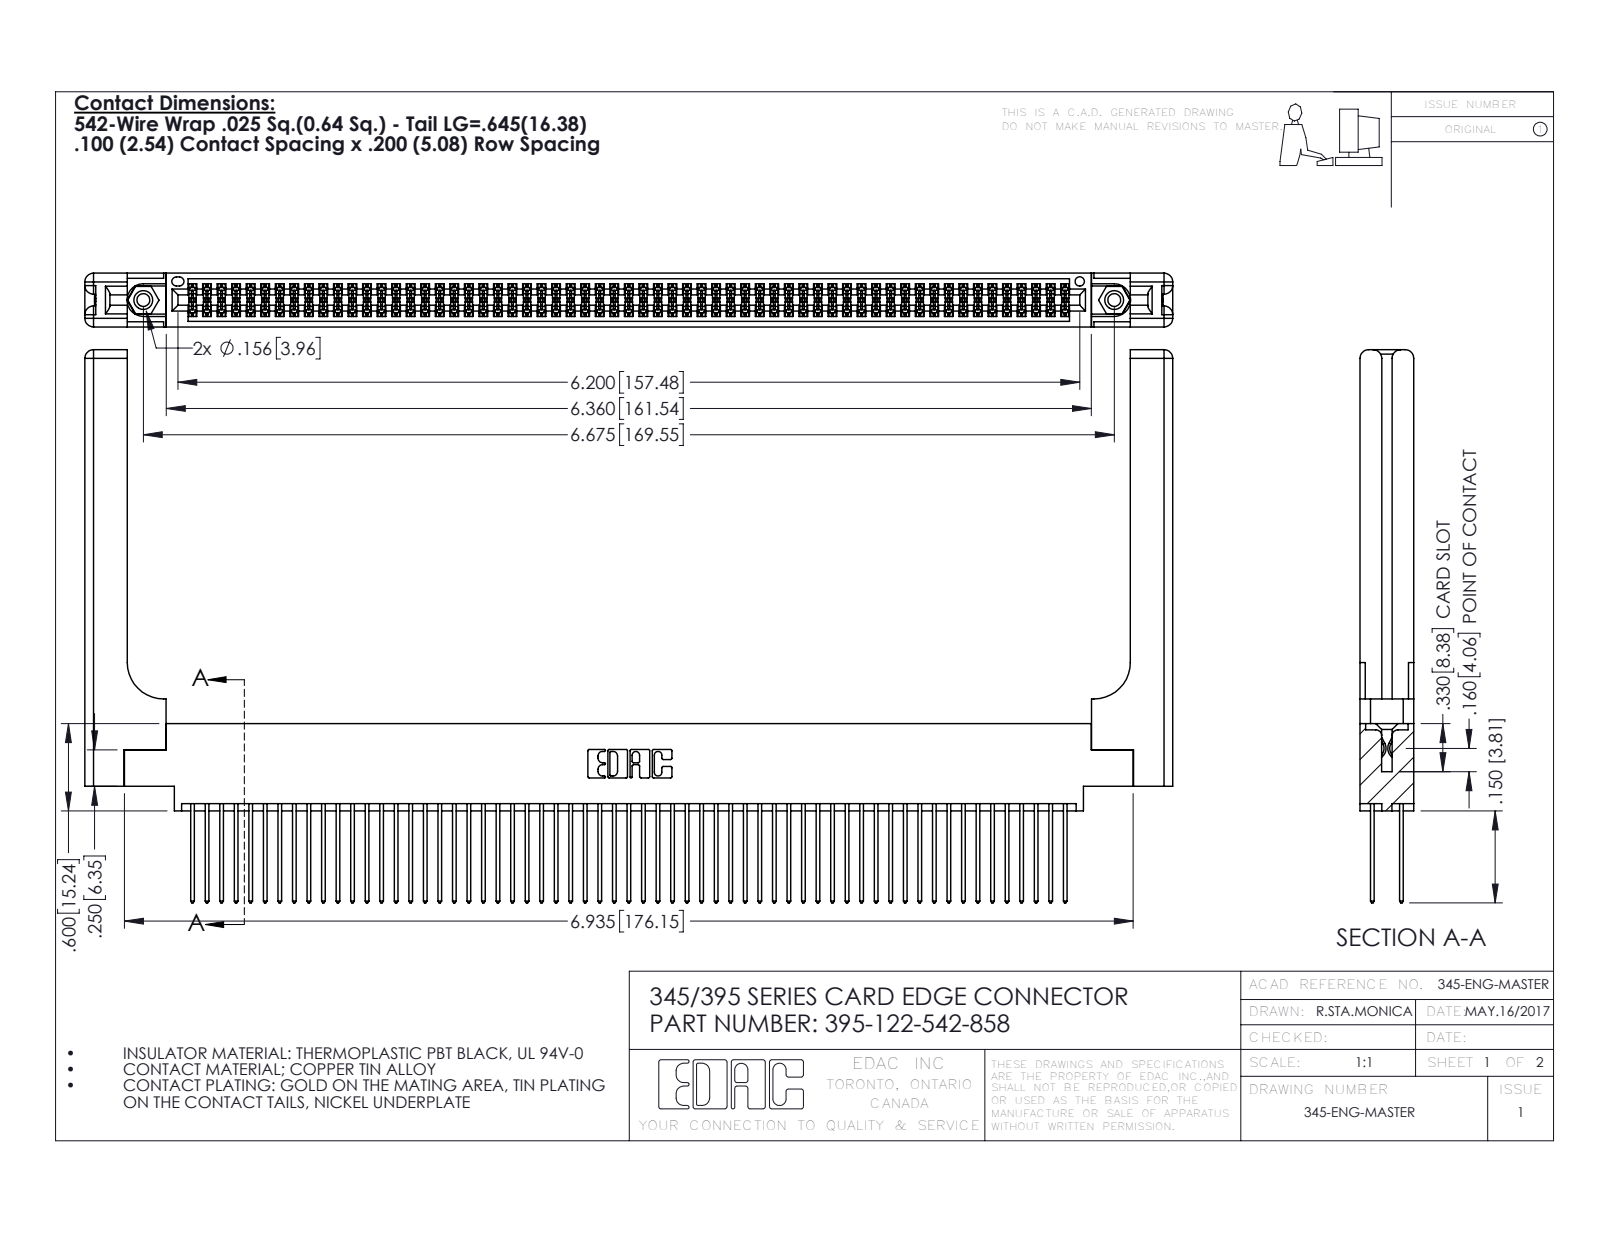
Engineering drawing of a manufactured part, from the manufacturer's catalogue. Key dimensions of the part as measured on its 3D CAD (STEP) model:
Part name (STEP PRODUCT): 345-250-001_345-250-001-102; 395-122-542-858; 345-220-058_345-220-058; 345-292-001_345-293-142 (+1 more)
STEP written by: SolidWorks 2016 (CONFIG_CONTROL_DESIGN)
Units: inches
Bodies: 127 solids, 6486 faces (4258 planar, 2168 cylindrical, 60 other)
Overall size (bounding box): 7.479 × 3.802 × 0.37
Volume: 1.682 in³ · Surface area: 56.48 in²
Round holes (diameter × count): ⌀0.089 ×2, ⌀0.125 ×2, ⌀0.156 ×2, ⌀0.064 ×1
Round bosses / shafts (diameter × count): ⌀0.155 ×2
Partial cylindrical surfaces — rounded edges, fillets, slot ends (radius × count): R0.006 ×183, R0.01 ×122, R0.01 ×22, R0.06 ×16, R0.007 ×6, R0.031 ×6, R0.026 ×3, R0.014 ×2
Main face-to-face distances: 0.072, 0.298, 0.37, 0.098, 0.272, 0.025, 0.2, 0.225, 0.175, 0.148
Hole centre spacings: 0.27, 6.439, 6.675
